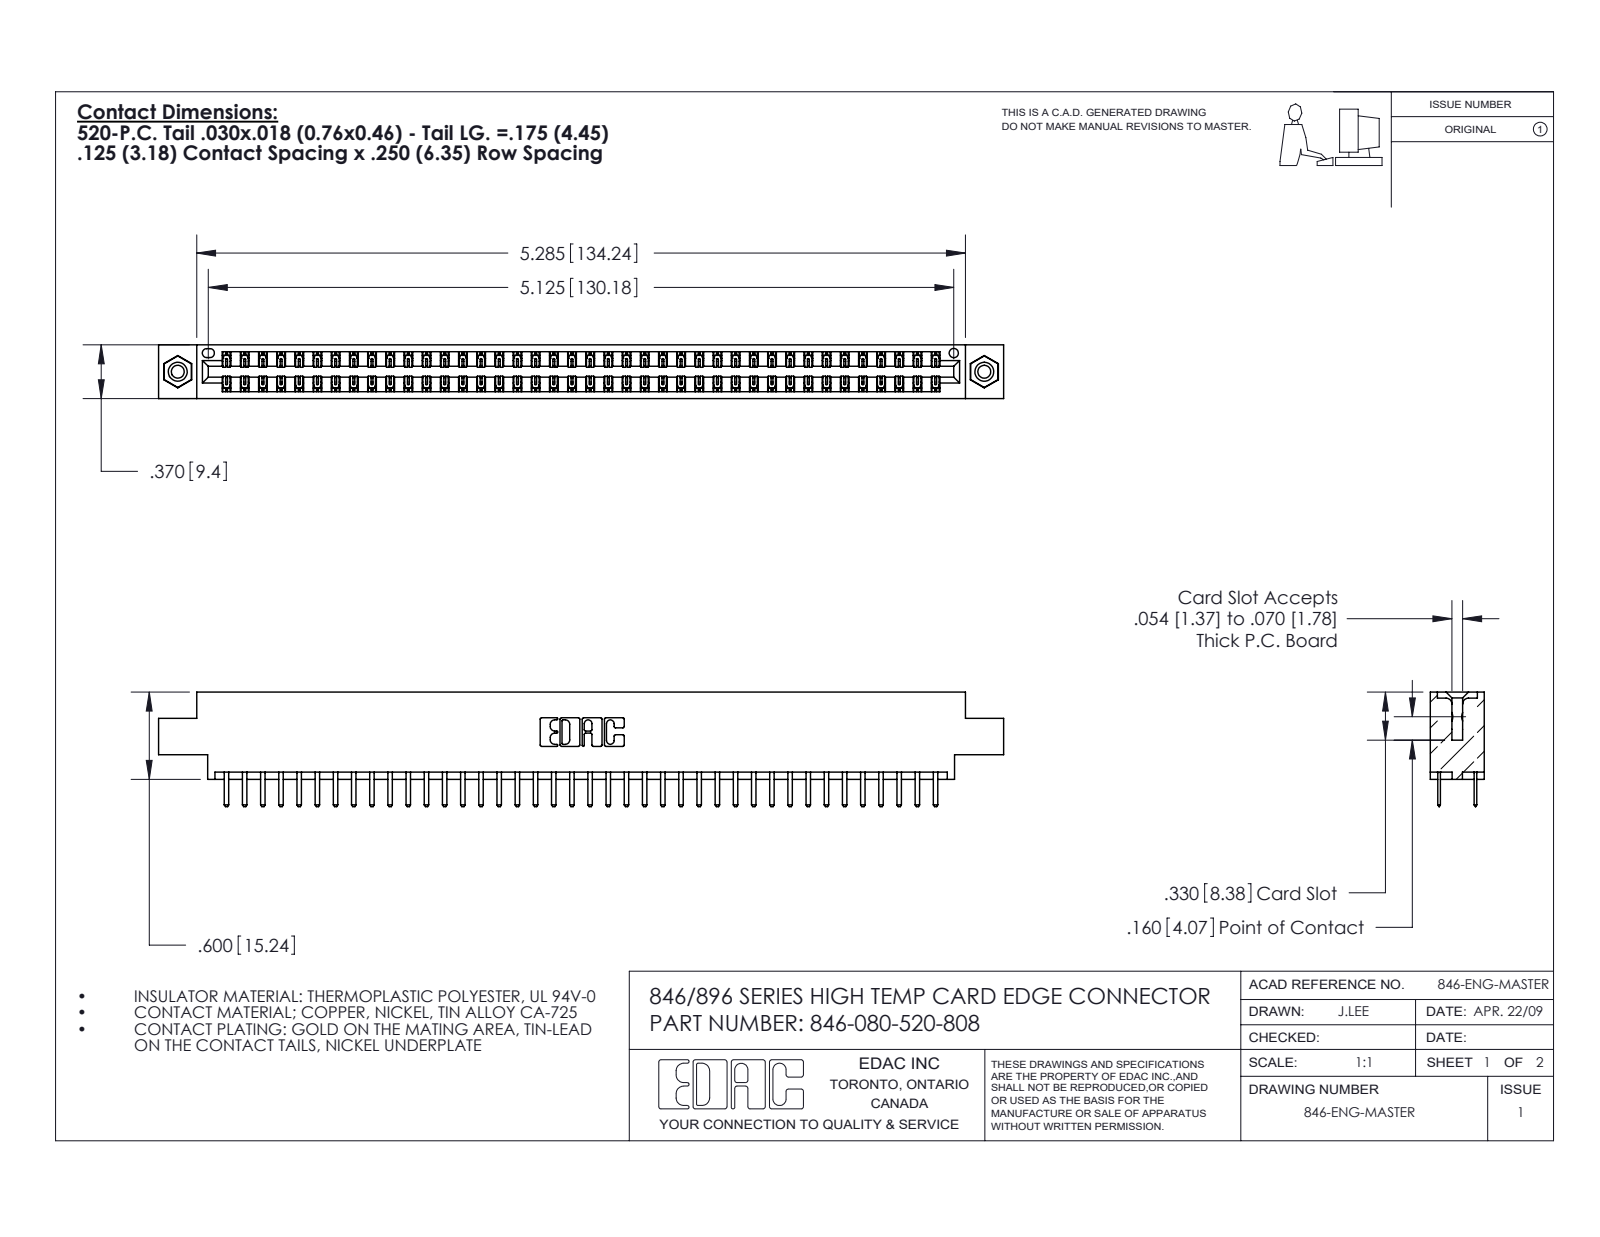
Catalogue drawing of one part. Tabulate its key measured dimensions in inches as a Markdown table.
| quantity | value |
| --- | --- |
| part name | 345-292-001_345-293-120; 345-250-001_345-250-003-102; 346-080-520-808; 346 Part_0.170 Offset - 0.156 Dia-TI |
| STEP written by | SolidWorks 2016 (CONFIG_CONTROL_DESIGN) |
| units | inches |
| bodies | 83 solids, 4666 faces (3072 planar, 1578 cylindrical, 16 other) |
| overall size | 5.81 × 0.788 × 0.37 |
| volume | 0.865 in³ |
| surface area | 30.34 in² |
| round holes (diameter × count) | 0.089 × 2, 0.125 × 2, 0.156 × 2, 0.064 × 1 |
| round bosses / shafts (diameter × count) | 0.155 × 2 |
| partial cylindrical surfaces (radius × count) | 0.006 × 120, 0.01 × 84, 0.01 × 22, 0.007 × 6, 0.031 × 6, 0.026 × 3, 0.014 × 2, 0.022 × 2 |
| main face-to-face distances | 0.048, 0.322, 0.25, 0.37, 0.275, 0.072, 0.298, 0.025, 0.222, 0.148 |
| hole center spacings | 0.246, 5.336, 5.545 |
